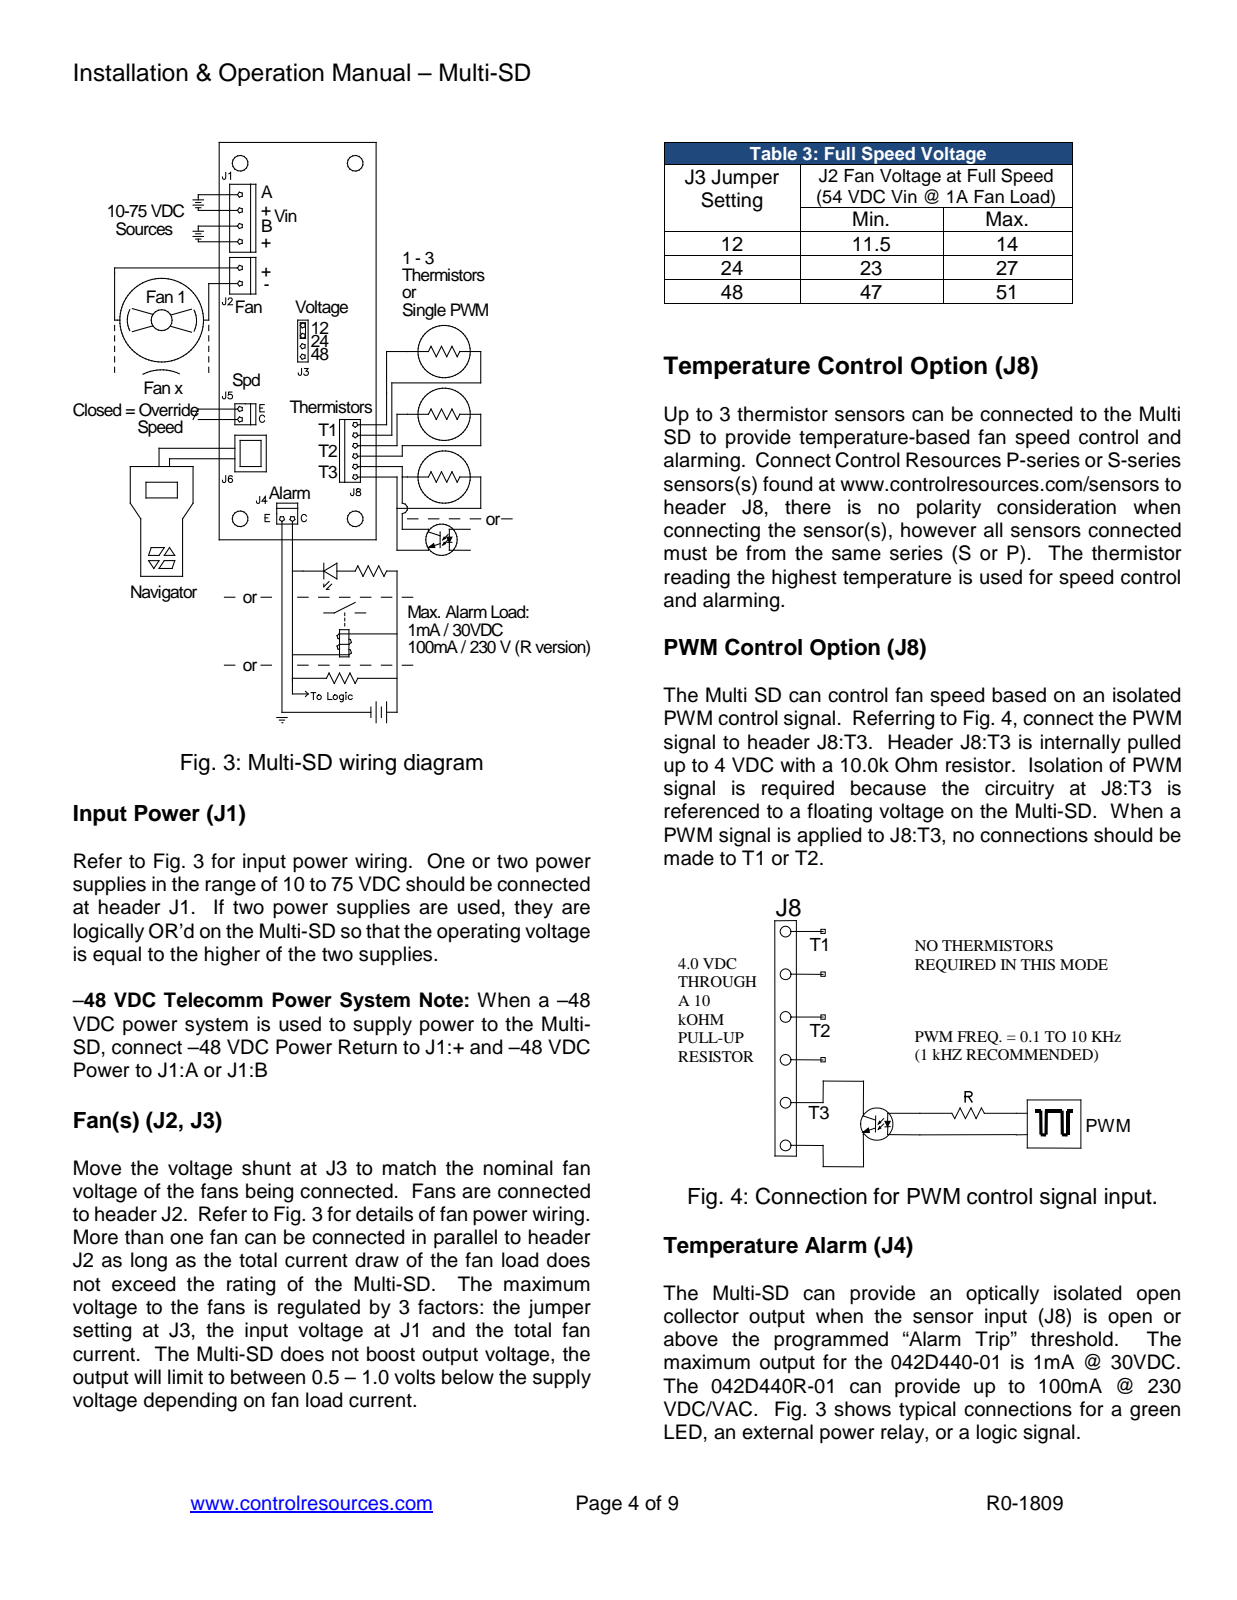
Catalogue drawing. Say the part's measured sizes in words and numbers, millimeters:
The part is named "sod-123f[sod-123f]; 44108[44108]; res_1206[res_1206]; res_0805[res_0805] (+8 more)". Its 3-D file was written by "KeyCreator (AUTOMOTIVE_DESIGN)". It is 198 solids with 8471 faces: 6316 planar, 1393 cylindrical and 762 other. Overall it measures 164.59 by 127 by 38.89 millimeters. Its volume is 46 914 cubic millimeters and its surface area 47 111 square millimeters. Round holes: 38 of diameter 0.46, 14 of diameter 1.02, 8 of diameter 0.89, 8 of diameter 1.42, 8 of diameter 1.7, 6 of diameter 0.36, 4 of diameter 0.91, 4 of diameter 3.96, 3 of diameter 0.99, 2 of diameter 1.17, 2 of diameter 3.25, 2 of diameter 8.4. Round bosses or shafts: 6 of diameter 0.6, 4 of diameter 1.07, 4 of diameter 0.81, 3 of diameter 0.4, 2 of diameter 20.57, 2 of diameter 15.49, 2 of diameter 12.5, 2 of diameter 11.6. Partial cylindrical surfaces (rounded edges, fillets, slot ends): 82 of radius 0.1, 64 of radius 0.15, 28 of radius 0.13, 28 of radius 0.25, 12 of radius 0.2, 12 of radius 0.3, 8 of radius 0.2, 8 of radius 0.47. The main face-to-face distances are 1.57, 3.1, 2.8, 3, 38.1, 5.02, 11.71, 16.73, 2.9, 1. The hole center spacings are 2.54, 5.08, 3.96, 2.03, 2.74, 3.97, 7.62, 2.73.
